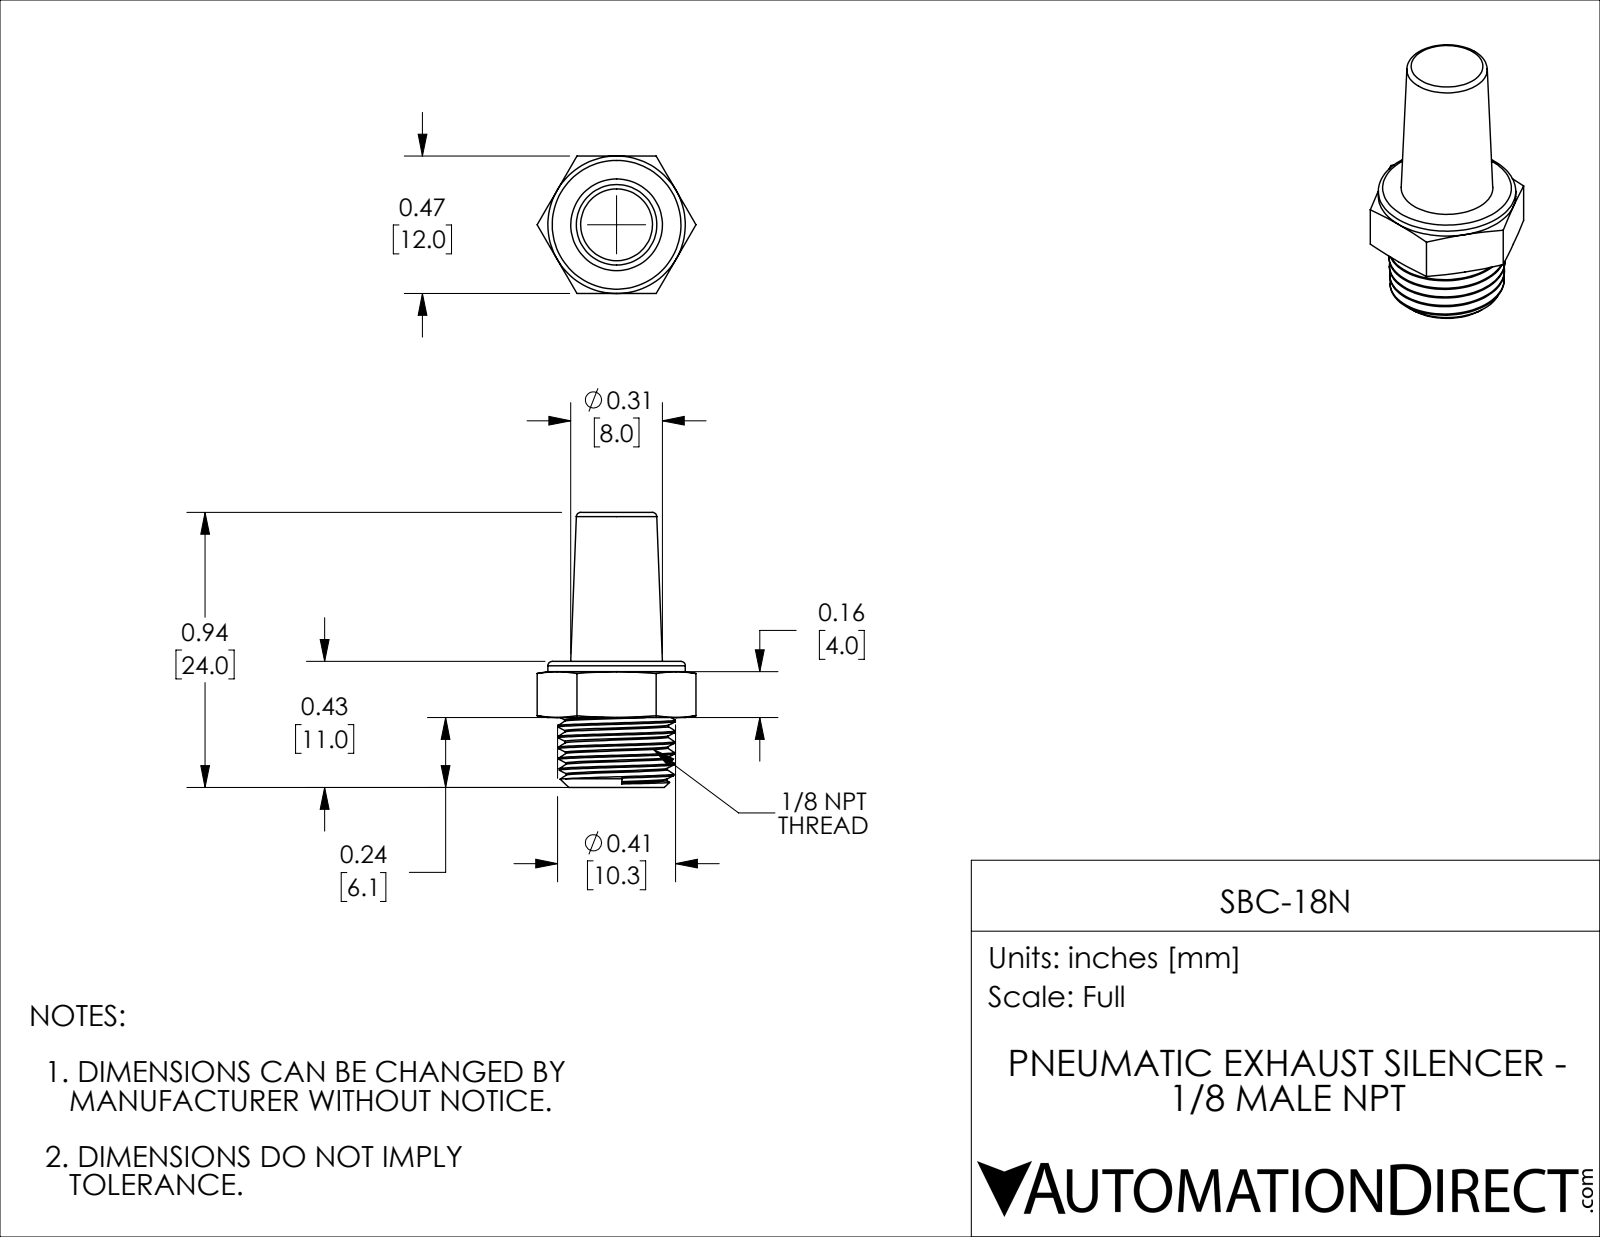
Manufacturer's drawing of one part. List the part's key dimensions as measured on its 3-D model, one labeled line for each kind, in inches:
Part name (STEP PRODUCT): SBC-18N
STEP written by: SolidWorks 2021 (CONFIG_CONTROL_DESIGN)
Units: inches
Bodies: 1 solid, 52 faces (12 planar, 4 cylindrical, 36 other)
Overall size (bounding box): 0.945 × 0.546 × 0.472
Volume: 0.083 in³ · Surface area: 1.817 in²
Round holes (diameter × count): ⌀0.25 ×1
Round bosses / shafts (diameter × count): ⌀0.472 ×1
Main face-to-face distances: 0.472, 0.193, 0.06, 0.133, 0.705, 0.645, 0.512, 0.24, 0.3, 0.433
